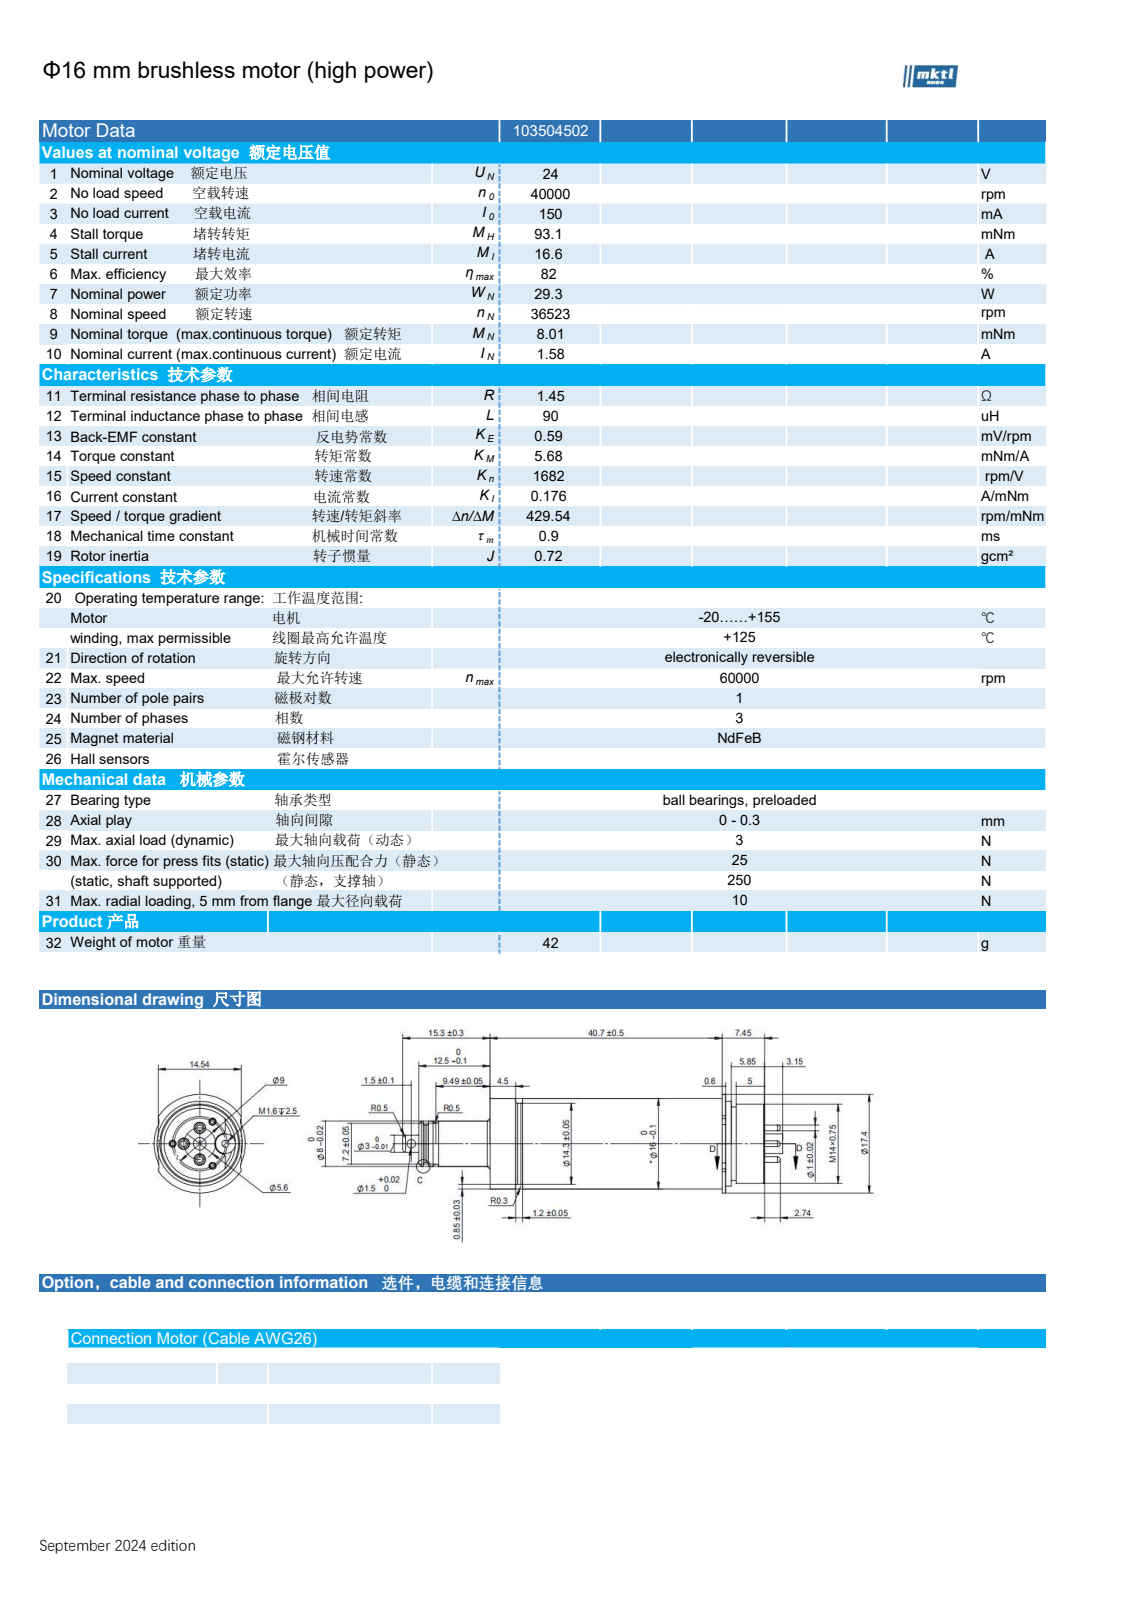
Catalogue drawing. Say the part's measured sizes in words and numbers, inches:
The part is named "approval 103504502". Its 3-D file was written by "SolidWorks 2018 (CONFIG_CONTROL_DESIGN)". It is 171 solids with 1308 faces: 399 planar, 833 cylindrical and 76 other. Overall it measures 2.622 by 0.685 by 0.63 inches. Its volume is 0.52 cubic inches and its surface area 57.07 square inches. Round holes: 4 of diameter 0.059, 3 of diameter 0.04, 3 of diameter 0.079, 1 of diameter 0.031, 1 of diameter 0.049, 1 of diameter 0.118, 1 of diameter 0.122, 1 of diameter 0.197, 1 of diameter 0.276, 1 of diameter 0.319, 1 of diameter 0.346, 1 of diameter 0.425. Round bosses or shafts: 3 of diameter 0.059, 3 of diameter 0.047, 3 of diameter 0.039, 3 of diameter 0.031, 3 of diameter 0.012, 1 of diameter 0.63, 1 of diameter 0.591, 1 of diameter 0.587. Partial cylindrical surfaces (rounded edges, fillets, slot ends): 20 of radius 0.02, 4 of radius 0.051, 1 of radius 0.074, 1 of radius 0.266, 1 of radius 0.343. The main face-to-face distances are 0.016, 0.024, 0.031, 0.039, 0.047, 0.055, 0.063, 0.071, 0.079, 0.087. The hole center spacings are 0.177, 0.11, 0.098, 0.156, 0.209, 0.219, 0.251, 0.278.
